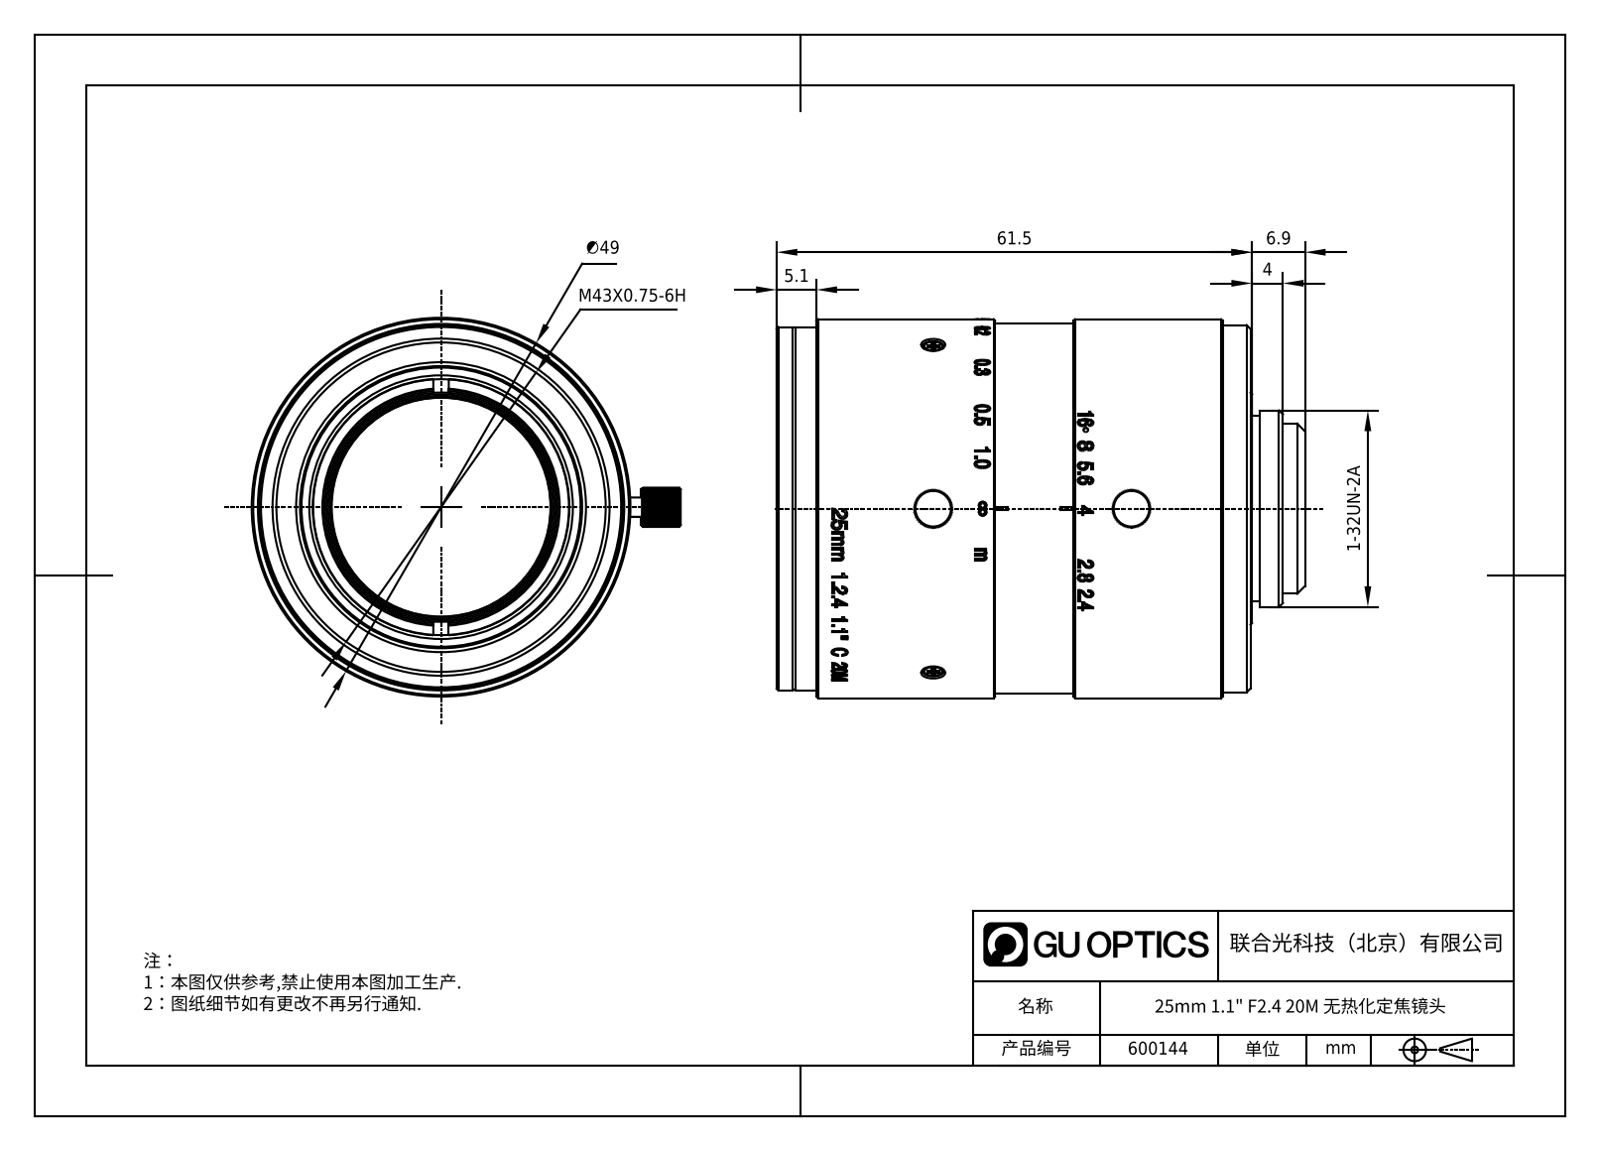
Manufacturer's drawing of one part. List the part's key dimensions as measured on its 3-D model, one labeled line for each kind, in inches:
Part name (STEP PRODUCT): 600145
STEP written by: SolidWorks 2020 (CONFIG_CONTROL_DESIGN)
Units: inches
Bodies: 0 solids, 2829 faces (872 planar, 701 cylindrical, 1256 other)
Overall size (bounding box): 2.691 × 2.185 × 1.929
Round holes (diameter × count): ⌀0.079 ×8, ⌀0.051 ×6, ⌀0.071 ×6, ⌀0.039 ×5, ⌀0.043 ×4, ⌀0.059 ×3, ⌀0.106 ×3, ⌀0.126 ×3, ⌀0.15 ×3, ⌀0.543 ×1, ⌀0.65 ×1, ⌀0.661 ×1
Round bosses / shafts (diameter × count): ⌀0.098 ×8, ⌀0.055 ×7, ⌀0.067 ×6, ⌀0.197 ×3, ⌀0.193 ×3, ⌀0.122 ×3, ⌀0.11 ×3, ⌀0.106 ×3
Partial cylindrical surfaces — rounded edges, fillets, slot ends (radius × count): R0.005 ×18, R0.012 ×18, R0.059 ×14, R0.03 ×8, R0.098 ×8, R0.02 ×7, R0.039 ×6, R0.053 ×6
Main face-to-face distances: 0.394, 0.346, 0.354, 0.4, 0.045, 1.673, 0.392, 2.028, 1.884, 1.929
Hole centre spacings: 0.222, 0.352, 0.435, 0.575, 0.669, 0.787, 1.01, 1.159
